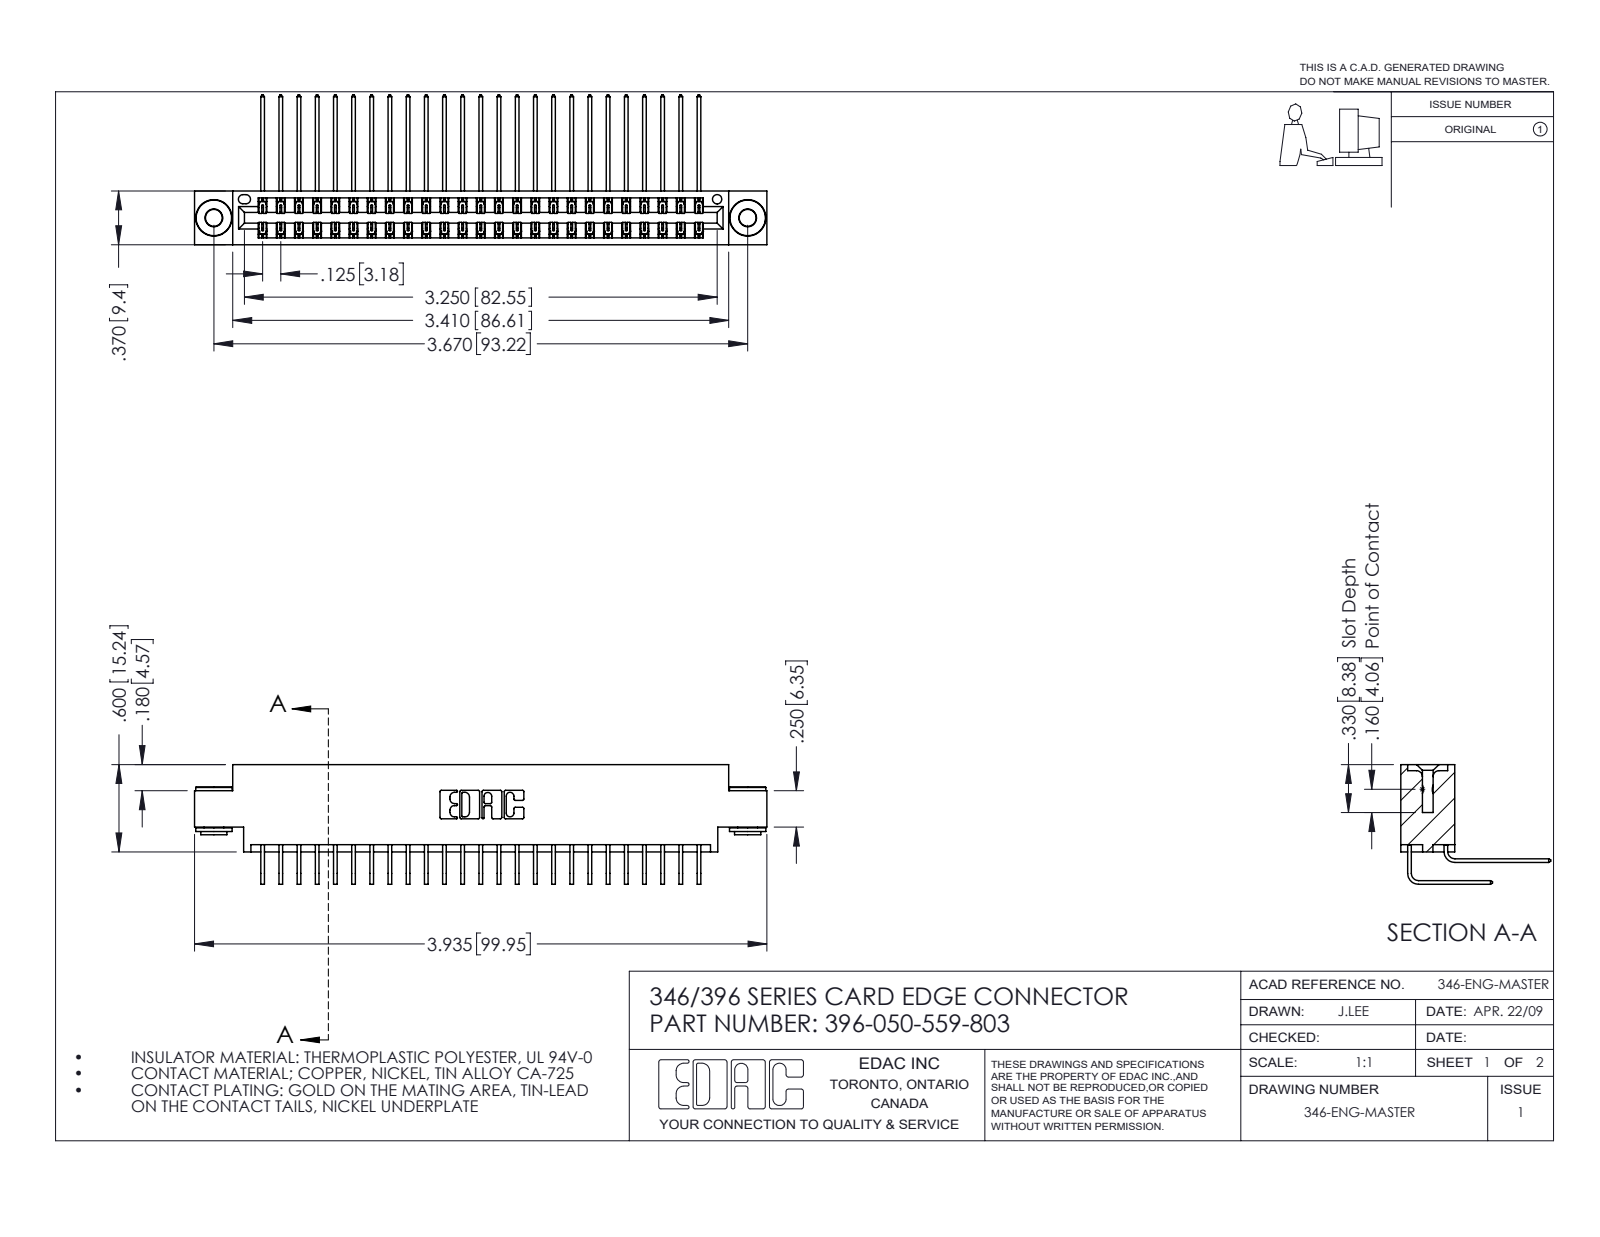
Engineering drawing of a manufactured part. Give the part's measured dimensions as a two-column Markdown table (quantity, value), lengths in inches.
| quantity | value |
| --- | --- |
| part name | 345-292-001_559 Tail - 2; 345-292-001_558 559 Tail - 1; 346 Part_0.170 Offset - 0.156 Dia-TH; 396-050-559-803 (+1 more) |
| STEP written by | SolidWorks 2016 (CONFIG_CONTROL_DESIGN) |
| units | inches |
| bodies | 53 solids, 2864 faces (1940 planar, 916 cylindrical, 8 other) |
| overall size | 3.935 × 1.03 × 0.823 |
| volume | 0.596 in³ |
| surface area | 23.15 in² |
| round holes (diameter × count) | 0.116 × 2, 0.156 × 2, 0.064 × 1 |
| round bosses / shafts (diameter × count) | 0.25 × 2, 0.18 × 2, 0.136 × 2 |
| partial cylindrical surfaces (radius × count) | 0.006 × 75, 0.01 × 22, 0.007 × 6, 0.031 × 6, 0.026 × 3, 0.014 × 2, 0.022 × 2, 0.024 × 2 |
| main face-to-face distances | 0.048, 0.322, 0.025, 0.37, 0.25, 0.072, 0.298, 0.275, 0.15, 0.148 |
| hole center spacings | 0.246, 3.462, 3.67 |
